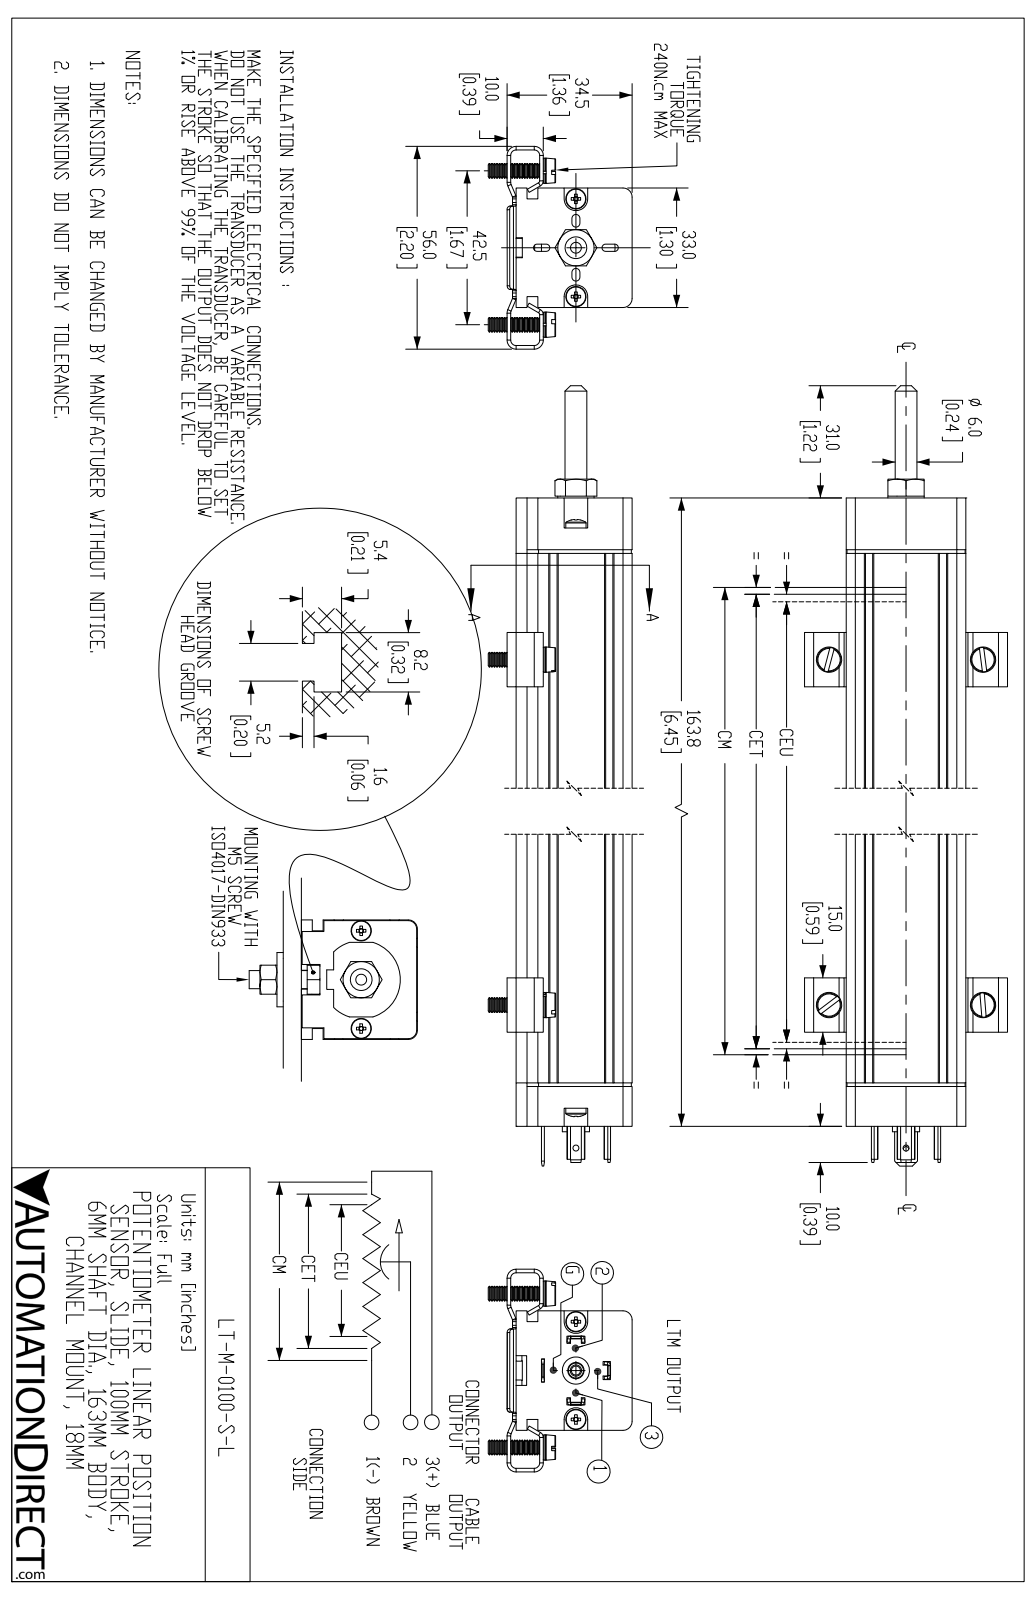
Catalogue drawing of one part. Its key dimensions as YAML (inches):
part_name: "LT-M-0100-S-L"
step_written_by: "SolidWorks 2019 (AUTOMOTIVE_DESIGN)"
units: inches
bodies: {solids: 21, faces: 1717, planar: 790, cylindrical: 365, other: 562}
overall_size: [8.102, 2.205, 1.563]
volume: 10.26
surface_area: 73.42
round_holes:
  - {diameter: 0.142, count: 4}
  - {diameter: 0.059, count: 2}
  - {diameter: 0.065, count: 2}
  - {diameter: 0.108, count: 2}
  - {diameter: 0.134, count: 2}
  - {diameter: 0.169, count: 2}
  - {diameter: 0.063, count: 1}
  - {diameter: 0.098, count: 1}
  - {diameter: 0.118, count: 1}
  - {diameter: 0.163, count: 1}
  - {diameter: 0.197, count: 1}
  - {diameter: 0.276, count: 1}
round_bosses_or_shafts:
  - {diameter: 0.274, count: 4}
  - {diameter: 0.157, count: 4}
  - {diameter: 0.22, count: 2}
  - {diameter: 0.118, count: 2}
  - {diameter: 0.394, count: 1}
  - {diameter: 0.295, count: 1}
  - {diameter: 0.236, count: 1}
  - {diameter: 0.177, count: 1}
partial_cylinders:
  - {radius: 0.039, count: 34}
  - {radius: 0.098, count: 12}
  - {radius: 0.059, count: 10}
  - {radius: 0.085, count: 8}
  - {radius: 0.033, count: 6}
  - {radius: 0.043, count: 4}
  - {radius: 0.024, count: 2}
  - {radius: 0.063, count: 2}
face_to_face_distances: [1.299, 1.26, 0.039, 0.118, 0.059, 1.287, 0.213, 0.02, 0.236, 0.488]
hole_center_spacings: [0.484, 0.531, 1.359, 1.663, 1.673, 1.765, 1.78, 3.372]
